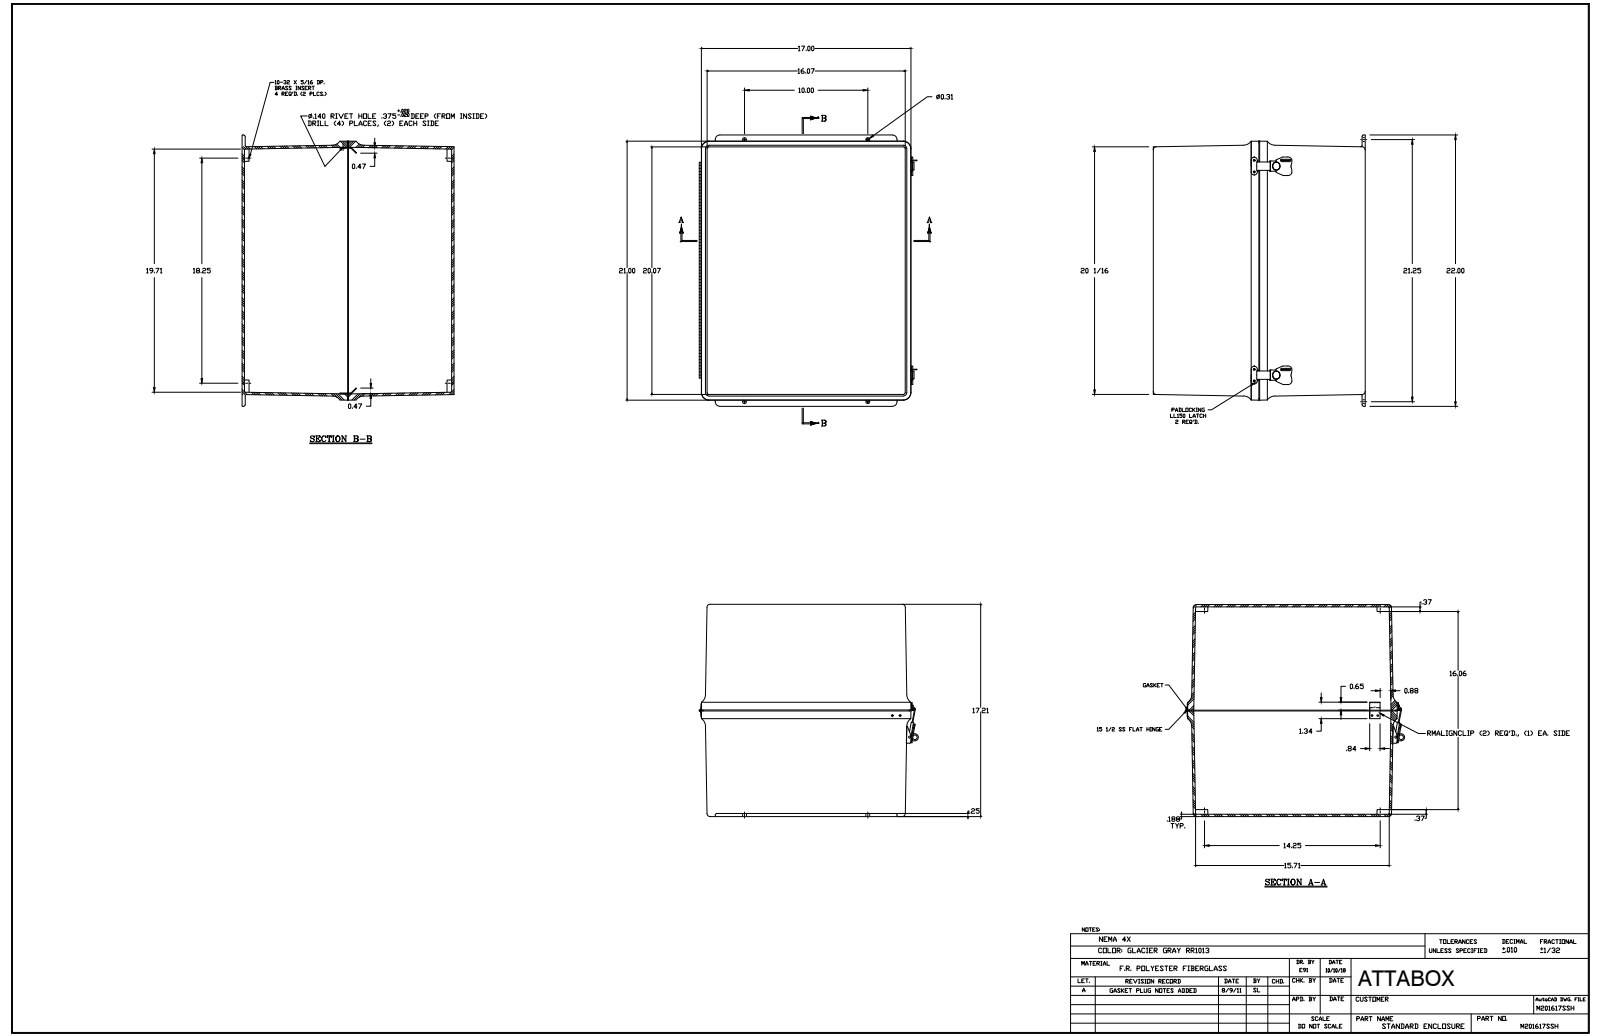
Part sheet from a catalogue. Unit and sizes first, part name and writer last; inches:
Units: inches
Overall size (bounding box): 22 × 17.741 × 17.184
Round holes (diameter × count): ⌀0.14 ×26, ⌀0.136 ×12, ⌀0.152 ×11, ⌀0.156 ×7, ⌀0.13 ×4, ⌀0.165 ×4, ⌀0.197 ×4, ⌀0.218 ×4, ⌀0.118 ×2, ⌀0.138 ×2, ⌀0.193 ×2, ⌀0.531 ×2
Round bosses / shafts (diameter × count): ⌀0.25 ×24, ⌀0.125 ×19, ⌀0.27 ×7, ⌀0.125 ×5, ⌀0.583 ×2, ⌀0.524 ×2, ⌀0.209 ×2, ⌀0.185 ×2
Partial cylindrical surfaces — rounded edges, fillets, slot ends (radius × count): R0.031 ×88, R0.079 ×19, R0.25 ×16, R0.75 ×14, R0.037 ×8, R0.039 ×8, R0.047 ×8, R0.062 ×8
Main face-to-face distances: 0.187, 16.189, 20.189, 16.001, 17.184, 0.188, 16.996, 16.997, 16.809, 16.376
Hole centre spacings: 3.75, 11, 17, 3.812, 7.25, 7.5, 14.75, 24.526
Volume: 392.8 in³ · Surface area: 3 982 in²
Bodies: 62 solids, 1759 faces (730 planar, 689 cylindrical, 340 other)
Part name (STEP PRODUCT): M201617SSH
STEP written by: SolidWorks 2018 (AUTOMOTIVE_DESIGN)
